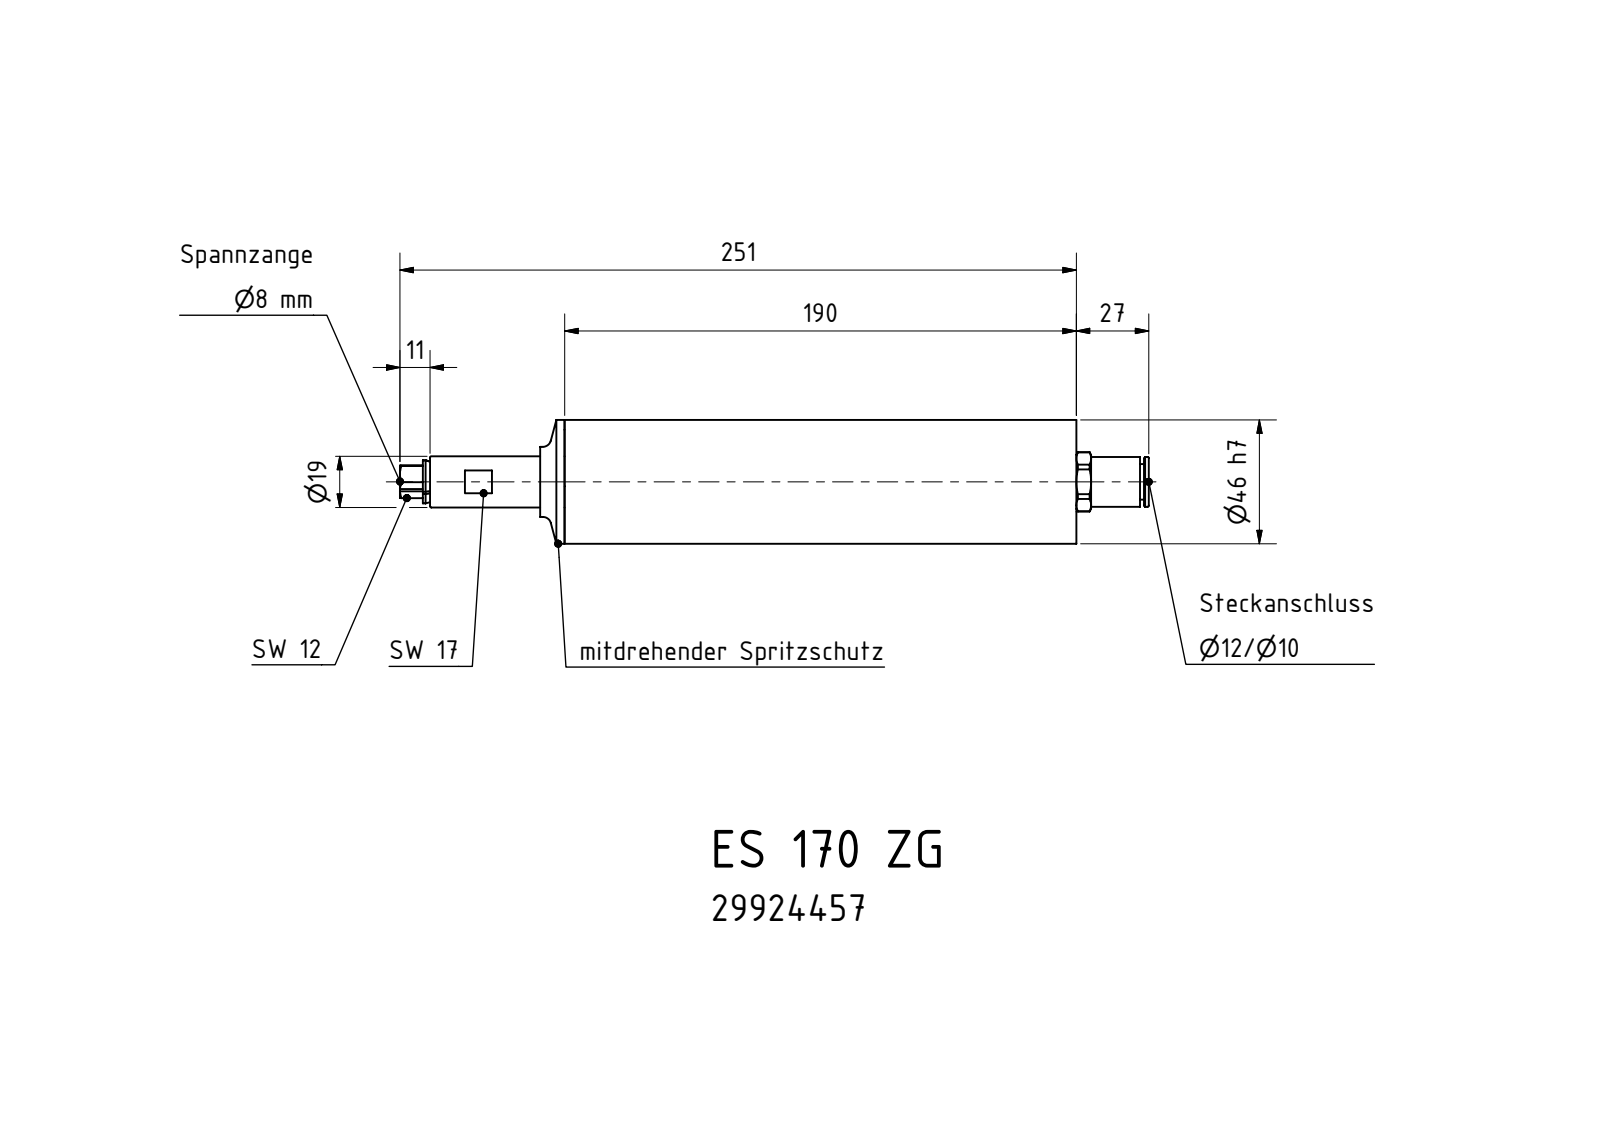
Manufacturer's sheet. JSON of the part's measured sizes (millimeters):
{"part_name": "ES 170 ZG_29924457", "step_written_by": "Autodesk Inventor 2008 (CONFIG_CONTROL_DESIGN)", "units": "millimeters", "bodies": {"solids": 1, "faces": 145, "planar": 73, "cylindrical": 38, "other": 34}, "overall_size": [278.06, 46, 46], "volume_mm3": 339352, "surface_area_mm2": 40137, "round_holes": [[8, 1], [8.5, 1], [10.92, 1], [12, 1], [12.1, 1], [15.1, 1], [19, 1]], "round_bosses_or_shafts": [[46, 1], [43.7, 1], [26, 1], [18.5, 1], [16, 1], [14.95, 1], [13.2, 1], [11.5, 1]], "partial_cylinders_radius": [[22.5, 3], [4.91, 1], [11, 1]], "face_to_face_distances": [9, 199.1, 197.77, 1.33, 197.67, 199, 9.1, 188.67, 190, 8.9]}
